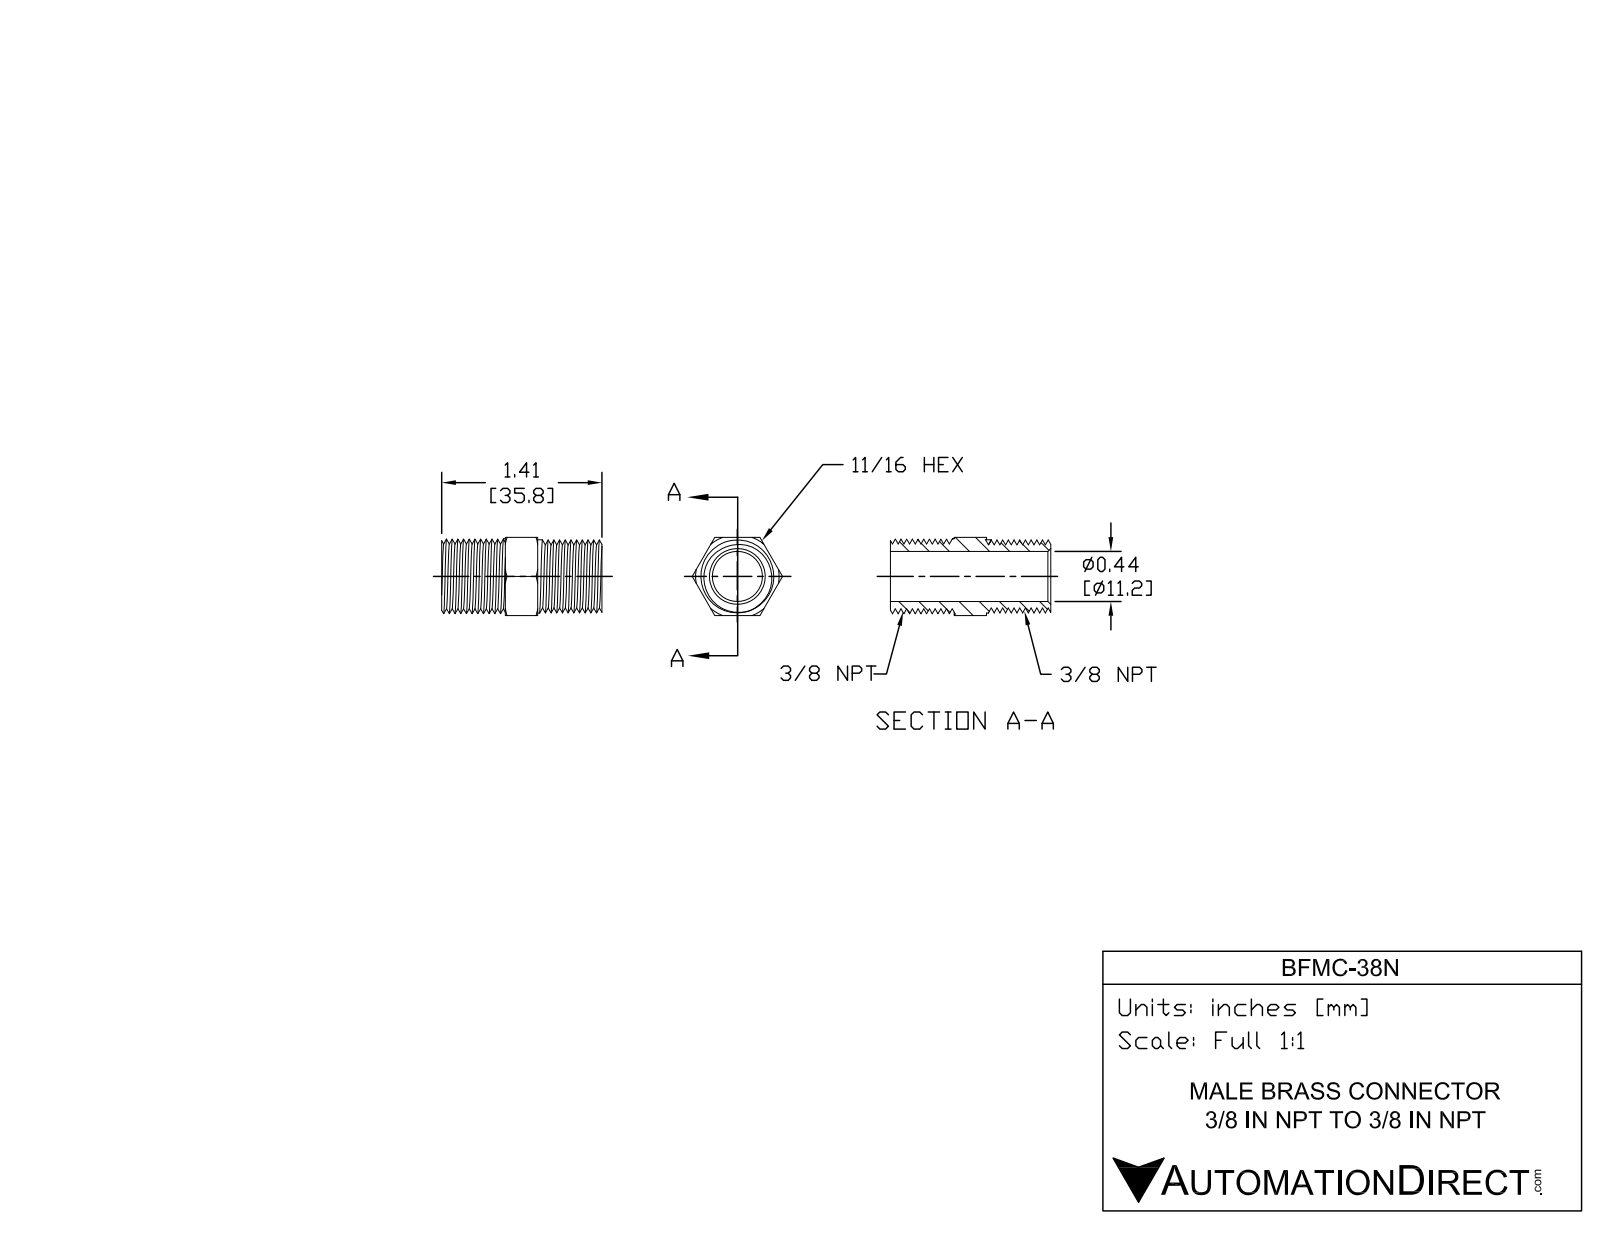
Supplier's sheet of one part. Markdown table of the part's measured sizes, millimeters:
| quantity | value |
| --- | --- |
| part name | BFMC-38N |
| STEP written by | SolidWorks 2015 (CONFIG_CONTROL_DESIGN) |
| units | millimeters |
| bodies | 1 solid, 44 faces (12 planar, 10 cylindrical, 22 other) |
| overall size | 35.8 × 20.2 × 17.5 |
| volume | 3 670 mm³ |
| surface area | 4 732 mm² |
| round holes (diameter × count) | 11.2 × 1, 16.9 × 1 |
| round bosses / shafts (diameter × count) | 16.4 × 1 |
| partial cylindrical surfaces (radius × count) | 8.3 × 1 |
| main face-to-face distances | 17.4, 35.8, 21.4, 14.4, 14.2, 7.2, 21.6 |
